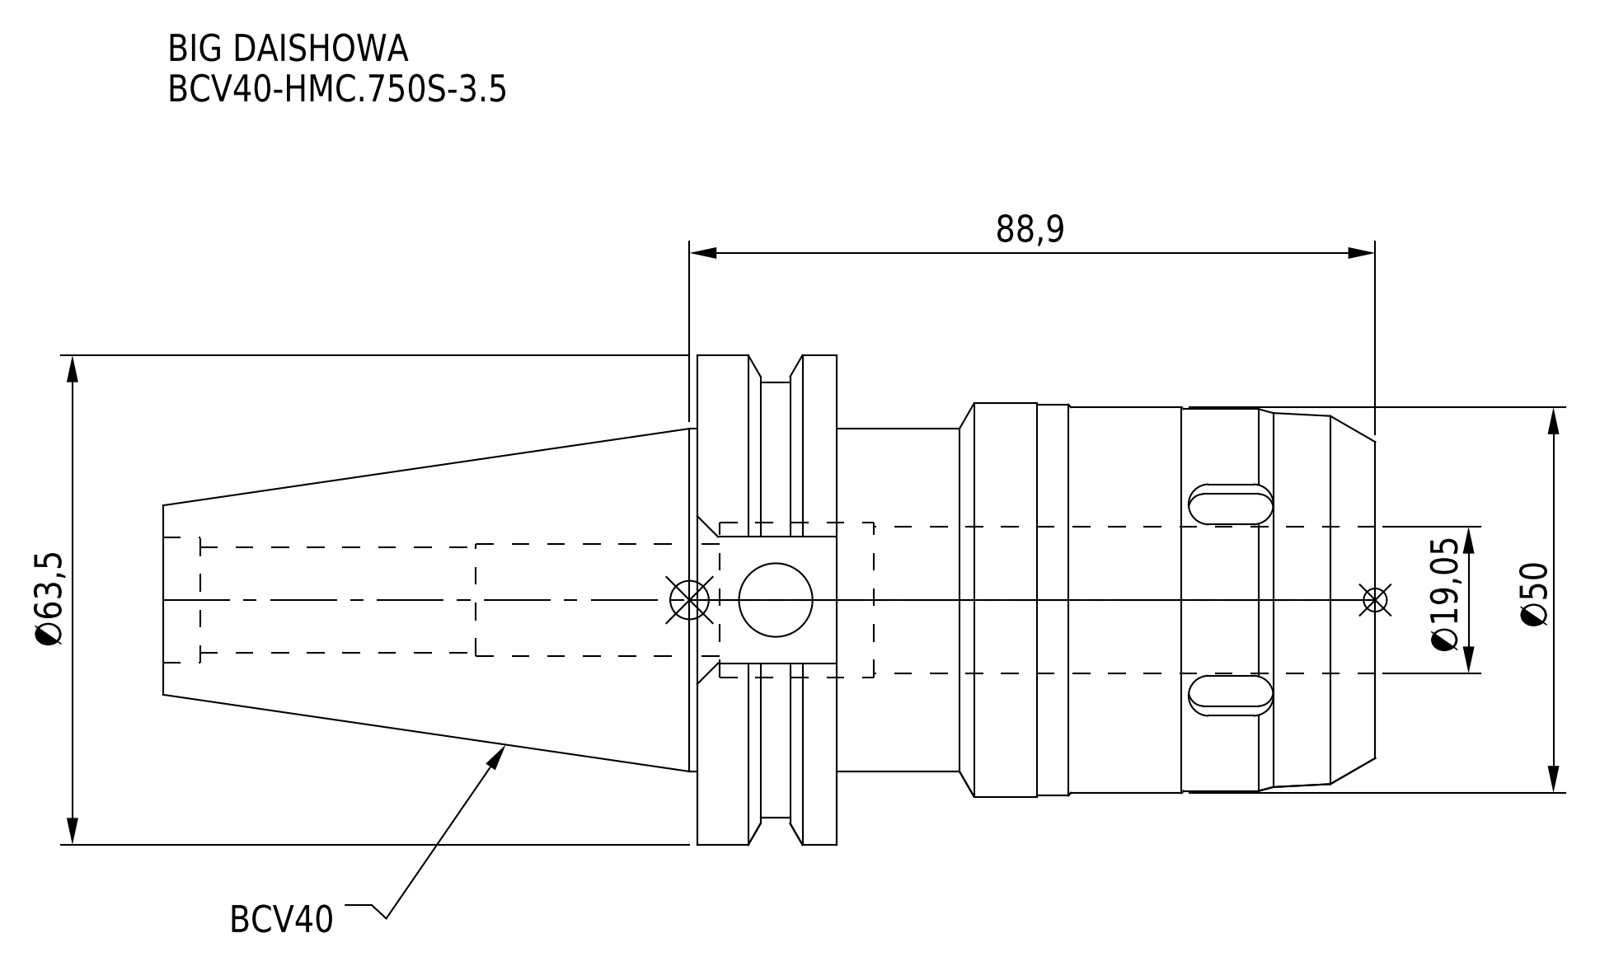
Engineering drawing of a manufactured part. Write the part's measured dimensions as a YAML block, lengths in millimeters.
part_name: "BCV40-HMC_750S-3_5"
step_written_by: "CREO PARAMETRIC BY PTC INC, 2016380 (AUTOMOTIVE_DESIGN)"
units: millimeters
bodies: {solids: 1, faces: 108, planar: 42, cylindrical: 44, other: 22}
overall_size: [157.15, 63.5, 61.35]
volume: 206907
surface_area: 36260
round_holes:
  - {diameter: 9.53, count: 1}
  - {diameter: 13.6, count: 1}
  - {diameter: 14.5, count: 1}
  - {diameter: 16.32, count: 1}
  - {diameter: 19.05, count: 1}
  - {diameter: 20.05, count: 1}
round_bosses_or_shafts:
  - {diameter: 63.5, count: 1}
  - {diameter: 56.36, count: 1}
  - {diameter: 51, count: 1}
  - {diameter: 50.7, count: 1}
  - {diameter: 50, count: 1}
  - {diameter: 49.5, count: 1}
  - {diameter: 44.45, count: 1}
partial_cylinders:
  - {radius: 3, count: 6}
face_to_face_distances: [18.05, 69.85, 87.9, 157.15, 87.3, 69.25, 47.55, 6, 45, 16.38]
